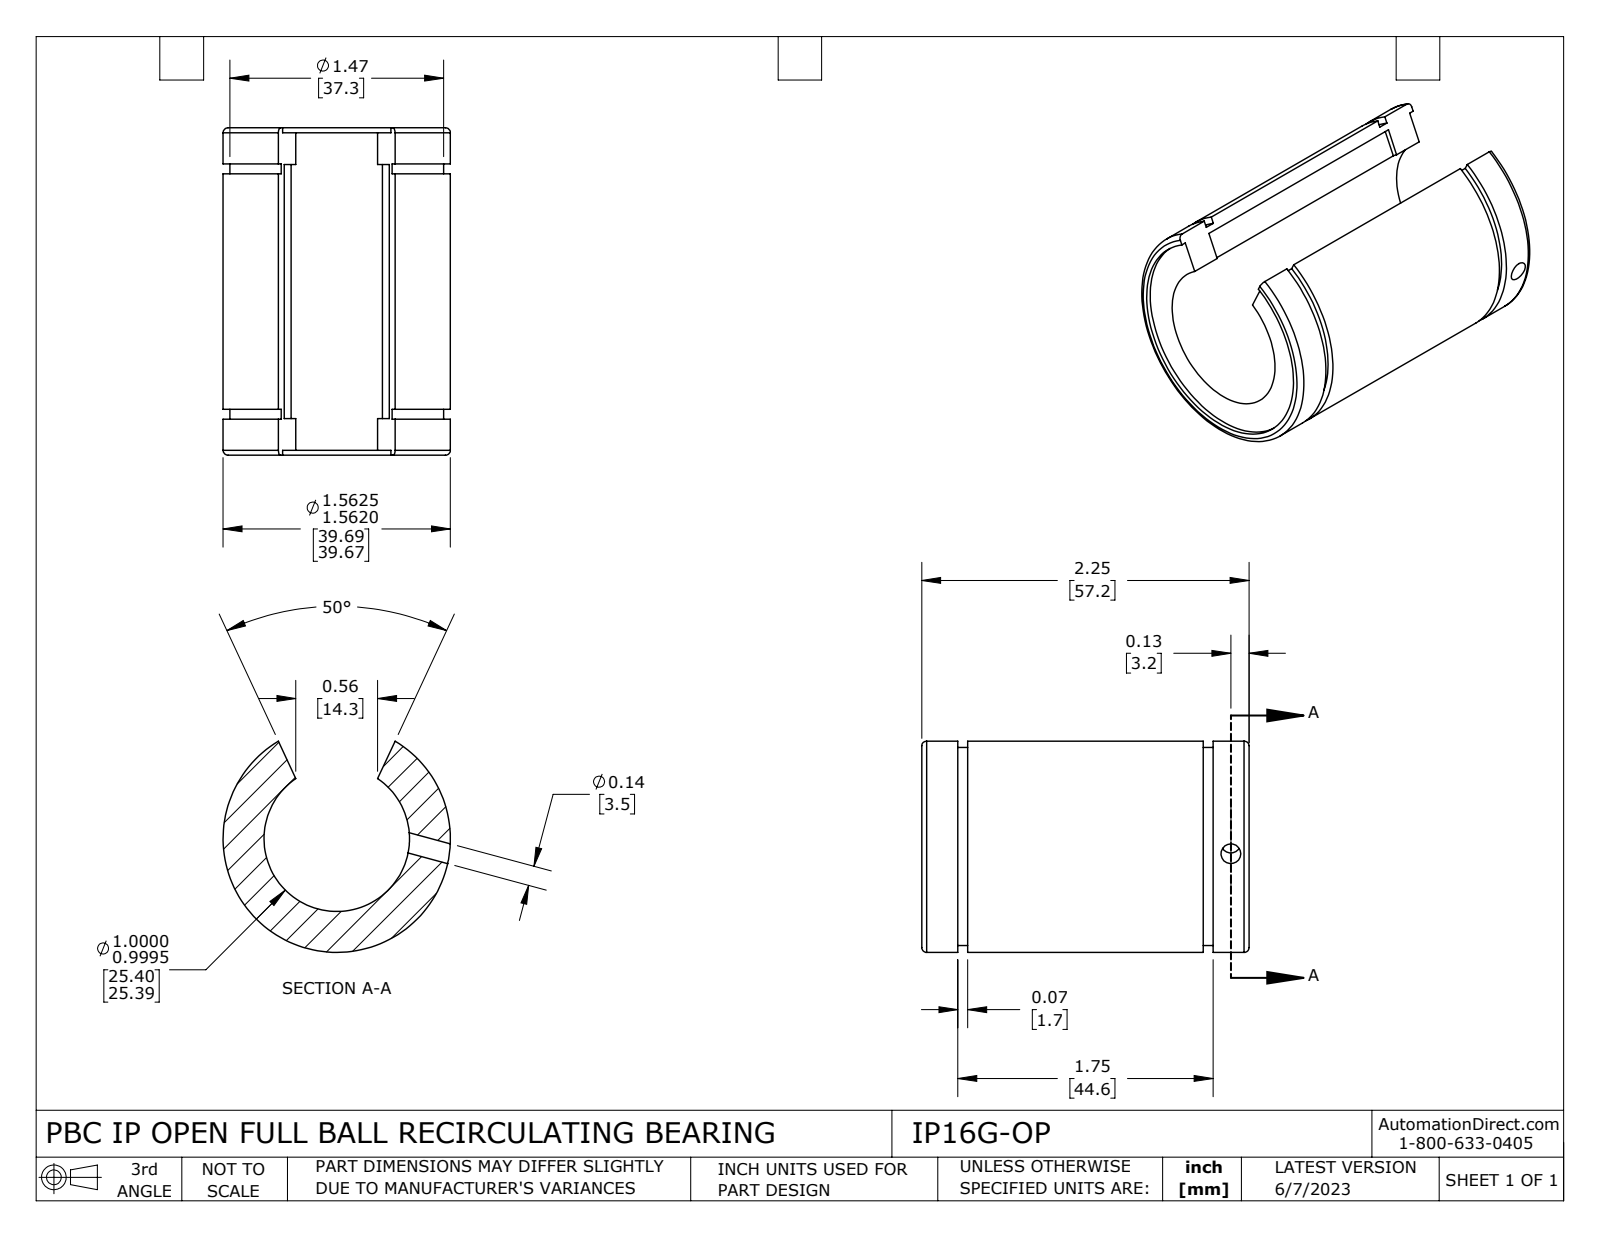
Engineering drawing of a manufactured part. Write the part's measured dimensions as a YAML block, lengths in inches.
part_name: "IP16G-OP"
step_written_by: "SolidWorks 2021 (CONFIG_CONTROL_DESIGN)"
units: inches
bodies: {solids: 1, faces: 40, planar: 16, cylindrical: 20, other: 4}
overall_size: [2.25, 1.563, 1.452]
volume: 1.989
surface_area: 18.76
round_holes:
  - {diameter: 0.136, count: 1}
  - {diameter: 1, count: 1}
  - {diameter: 1.427, count: 1}
round_bosses_or_shafts:
  - {diameter: 1.563, count: 1}
  - {diameter: 1.469, count: 1}
partial_cylinders:
  - {radius: 0.687, count: 1}
face_to_face_distances: [2.182, 0.281, 1.9, 0.214, 1.968, 0.068, 1.687, 0.04, 0.04, 0.034]
